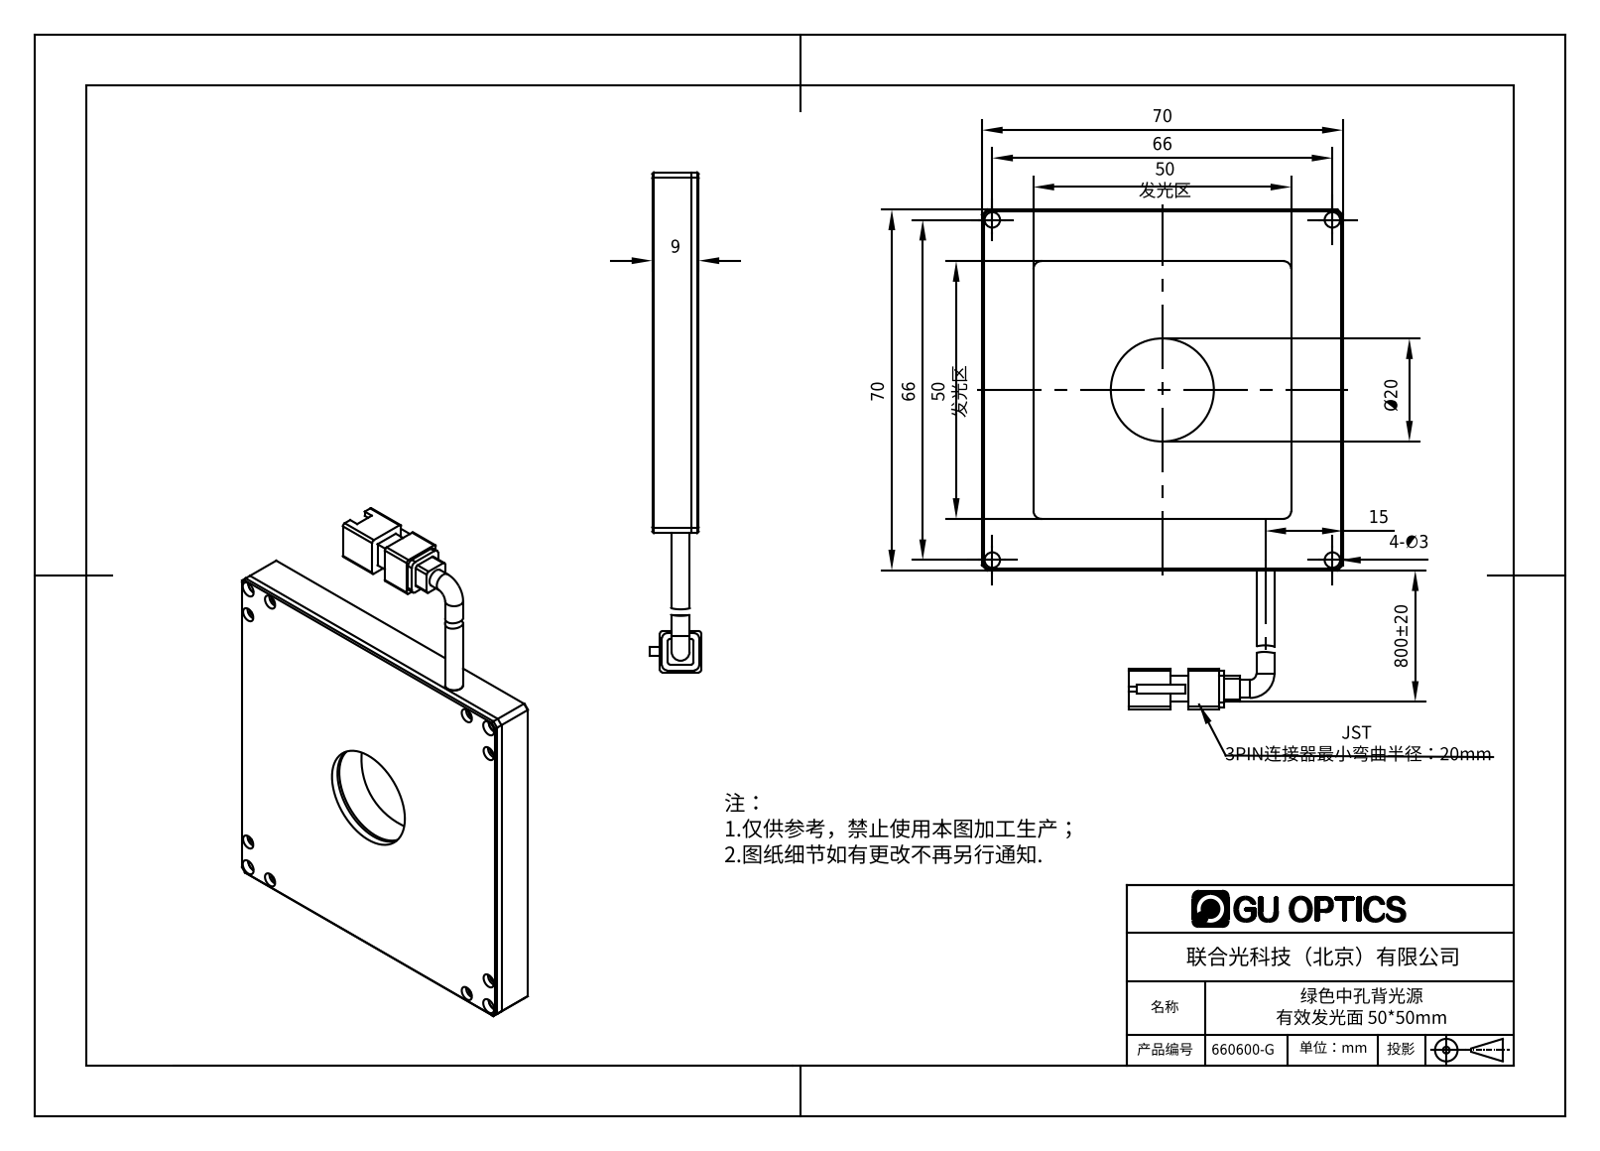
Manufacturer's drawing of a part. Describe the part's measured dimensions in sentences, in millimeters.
The part is named "660600-G". Its 3-D file was written by "SolidWorks 2016 (AUTOMOTIVE_DESIGN)". It is 7 solids with 501 faces: 306 planar, 118 cylindrical and 77 other. Overall it measures 97 by 70 by 10 millimeters. Its volume is 34 282 cubic millimeters and its surface area 29 900 square millimeters. Round holes: 10 of diameter 1.6, 8 of diameter 1.25, 8 of diameter 2.8, 4 of diameter 3, 1 of diameter 20. Round bosses or shafts: 2 of diameter 3.5. Partial cylindrical surfaces (rounded edges, fillets, slot ends): 8 of radius 0.5, 6 of radius 2, 4 of radius 1, 4 of radius 1.5. The main face-to-face distances are 6.5, 6, 1.5, 8, 2, 1, 0.5, 3, 7, 7.5. The hole center spacings are 66, 42.64, 60.3, 66.27, 89.2, 6, 60, 85.28.
